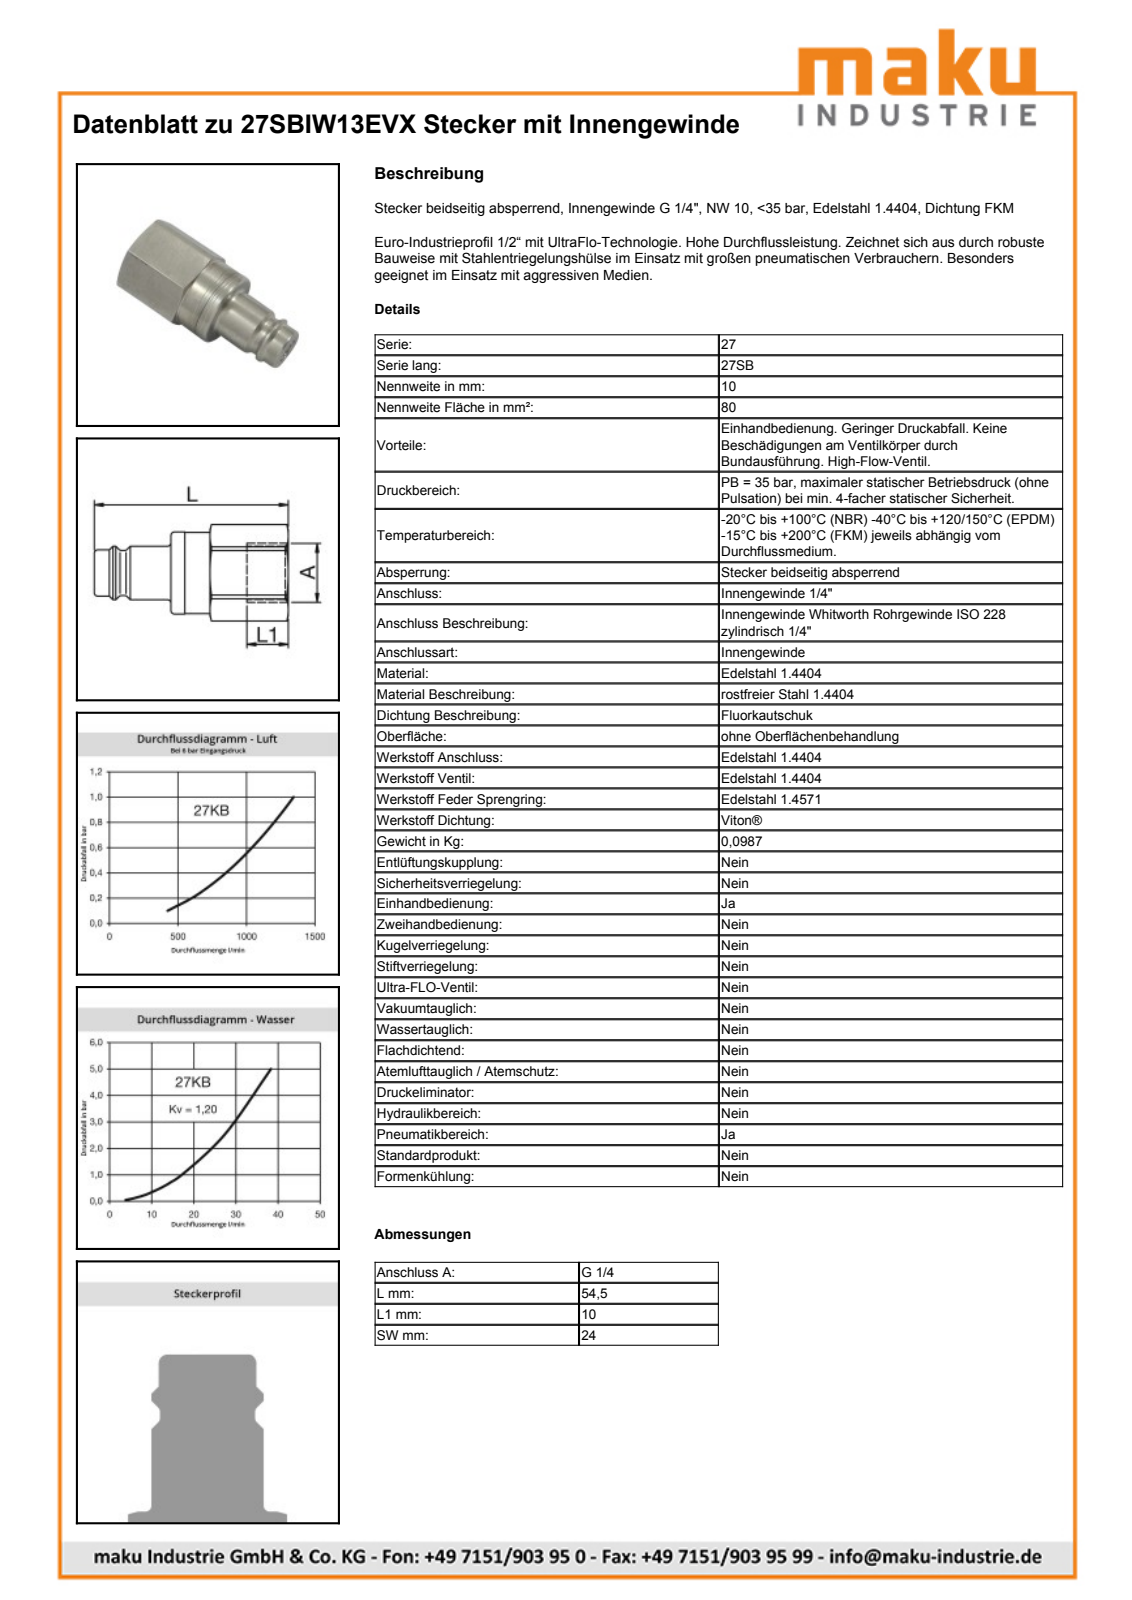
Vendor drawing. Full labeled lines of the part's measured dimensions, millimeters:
Part name (STEP PRODUCT): D108507
STEP written by: Autodesk Inventor 2013 (AUTOMOTIVE_DESIGN)
Units: millimetres
Bodies: 1 solid, 57 faces (14 planar, 18 cylindrical, 25 other)
Overall size (bounding box): 54.4 × 26.95 × 25.41
Volume: 17 853 mm³ · Surface area: 5 544 mm²
Round holes (diameter × count): ⌀11.45 ×1, ⌀19 ×1, ⌀20.3 ×1
Round bosses / shafts (diameter × count): ⌀23 ×1, ⌀22.75 ×1, ⌀18.65 ×1, ⌀18.5 ×1, ⌀15 ×1, ⌀13 ×1, ⌀12.65 ×1
Partial cylindrical surfaces — rounded edges, fillets, slot ends (radius × count): R13.53 ×1
Main face-to-face distances: 24, 32.9, 24.58, 8.32, 21.5, 46.08, 54.4, 25.4, 3.9, 20.68
